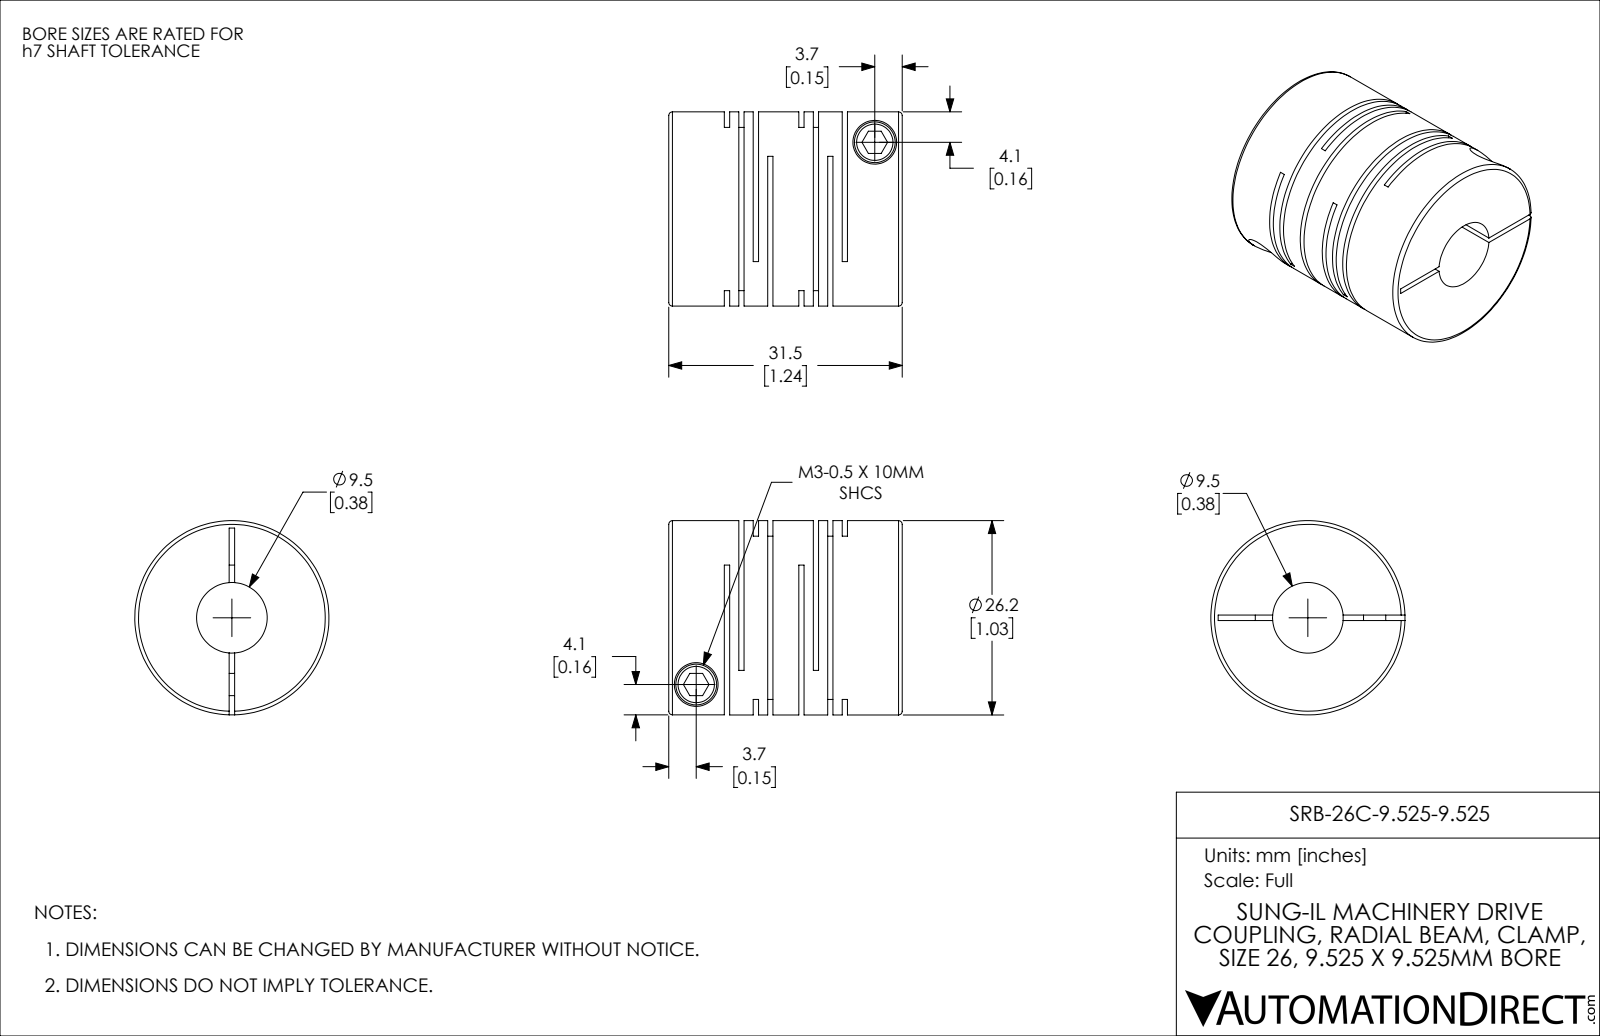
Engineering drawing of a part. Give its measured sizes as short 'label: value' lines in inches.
name: SRB-26C-9.525-9.525
written by: SolidWorks 2021 (CONFIG_CONTROL_DESIGN)
unit: in
bodies: 1 solid, 114 faces (60 planar, 42 cylindrical, 12 other)
size: 1.24 × 1.031 × 1.031
volume: 0.74 in³; area: 16.79 in²
holes: 2× ⌀0.118, 2× ⌀0.232, 1× ⌀0.375
bosses: 2× ⌀0.217, 1× ⌀1.031
face distances: 0.077, 0.396, 0.028, 0.154, 0.319, 0.472, 0.049, 0.105, 0.368, 0.549
